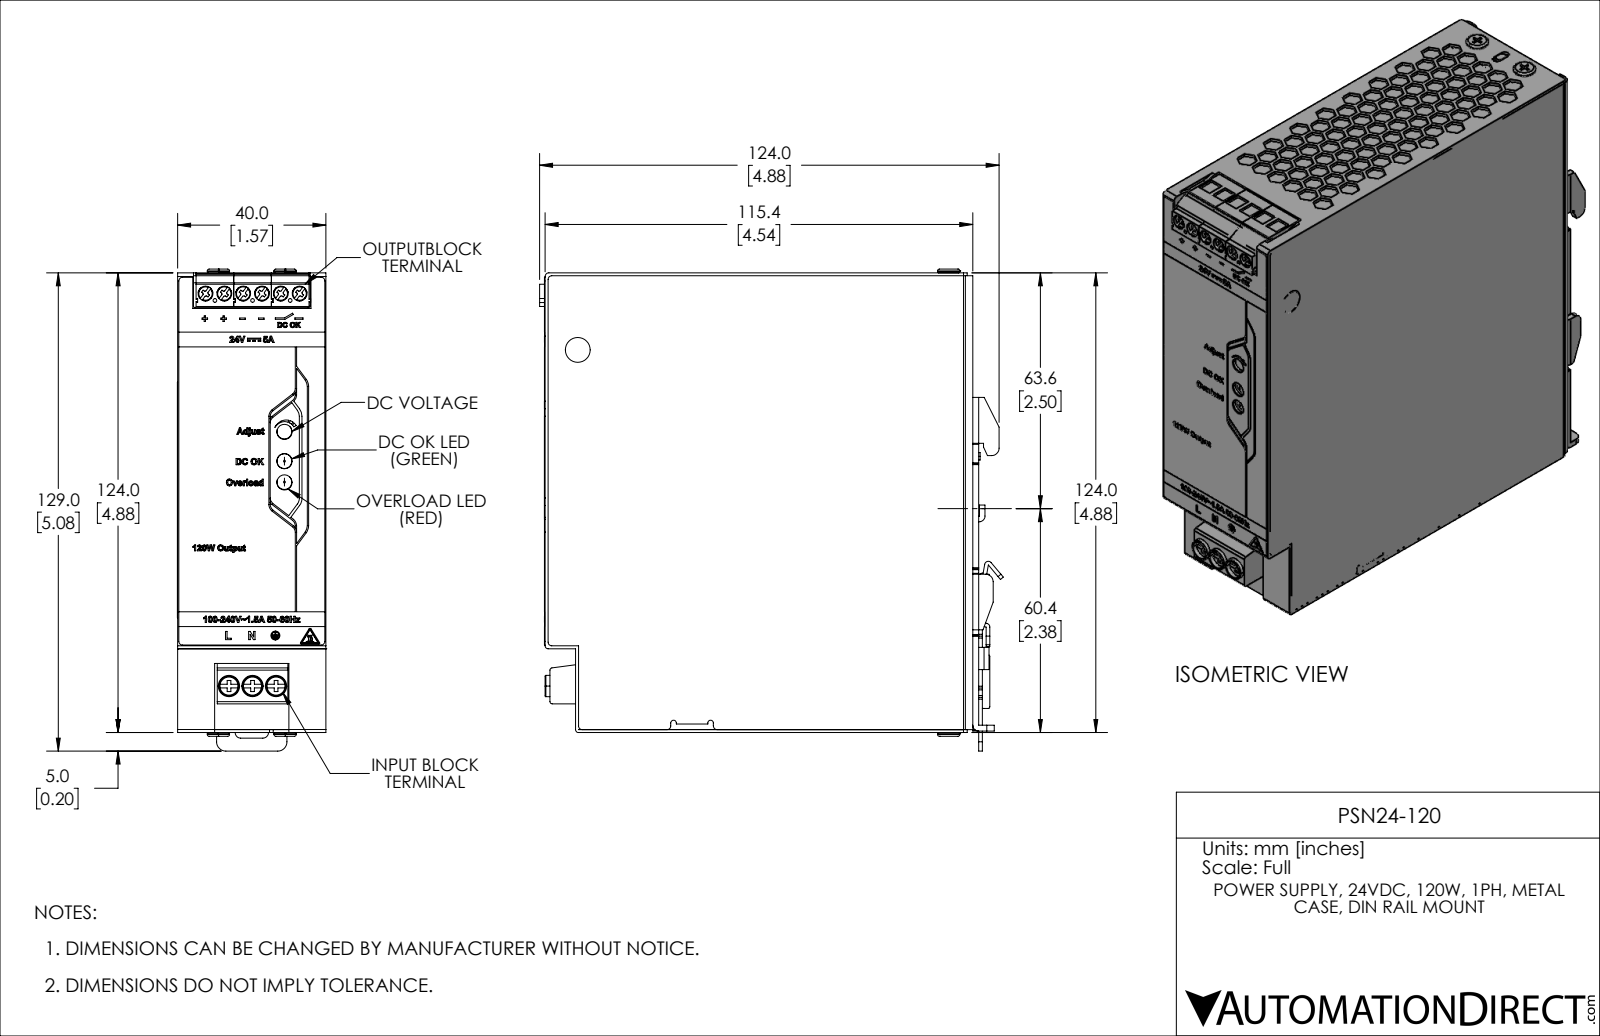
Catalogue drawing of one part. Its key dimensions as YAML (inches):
part_name: "PSN24-120_WESLEY"
step_written_by: "SolidWorks 2021 (CONFIG_CONTROL_DESIGN)"
units: inches
bodies: {solids: 27, faces: 2162, planar: 1229, cylindrical: 263, other: 670}
overall_size: [5.118, 4.927, 1.575]
volume: 34.98
surface_area: 126.1
round_holes:
  - {diameter: 0.157, count: 6}
  - {diameter: 0.154, count: 4}
  - {diameter: 0.138, count: 3}
  - {diameter: 0.193, count: 3}
  - {diameter: 0.039, count: 2}
  - {diameter: 0.102, count: 1}
round_bosses_or_shafts:
  - {diameter: 0.236, count: 6}
  - {diameter: 0.118, count: 4}
  - {diameter: 0.226, count: 3}
  - {diameter: 0.079, count: 2}
  - {diameter: 0.163, count: 1}
partial_cylinders:
  - {radius: 0.01, count: 50}
  - {radius: 0.02, count: 37}
  - {radius: 0.012, count: 24}
  - {radius: 0.039, count: 10}
  - {radius: 0.063, count: 6}
  - {radius: 0.079, count: 6}
  - {radius: 0.017, count: 2}
  - {radius: 0.024, count: 2}
face_to_face_distances: [1.575, 4.543, 4.512, 4.882, 0.031, 0.063, 0.017, 0.048, 4.558, 4.55]
hole_center_spacings: [0.2, 0.4, 0.6, 0.787, 0.25, 0.295, 0.364, 0.466]
